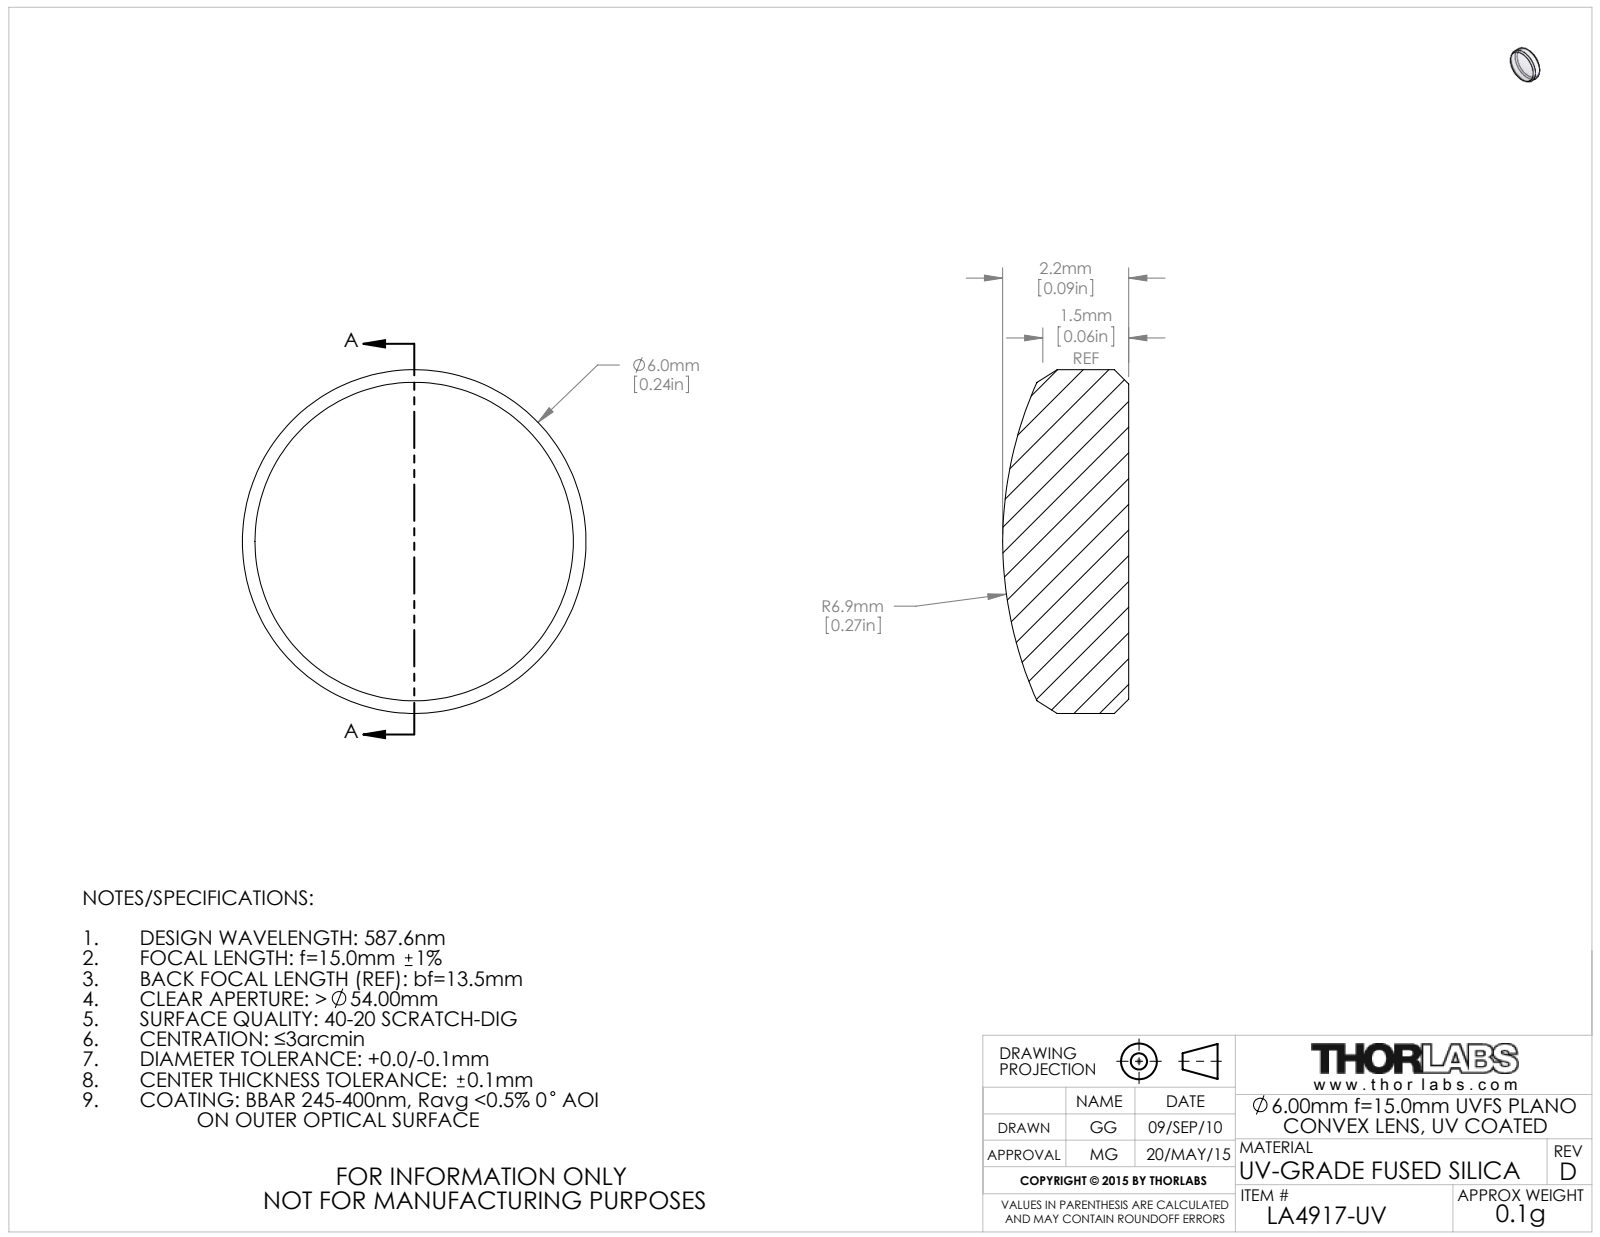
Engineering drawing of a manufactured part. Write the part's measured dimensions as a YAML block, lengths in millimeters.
part_name: "4269-E0W"
step_written_by: "SolidWorks 2014 (CONFIG_CONTROL_DESIGN)"
units: millimeters
bodies: {solids: 1, faces: 9, planar: 1, cylindrical: 2, other: 6}
overall_size: [6, 6, 2.2]
volume: 51
surface_area: 82
round_bosses_or_shafts:
  - {diameter: 6, count: 1}
